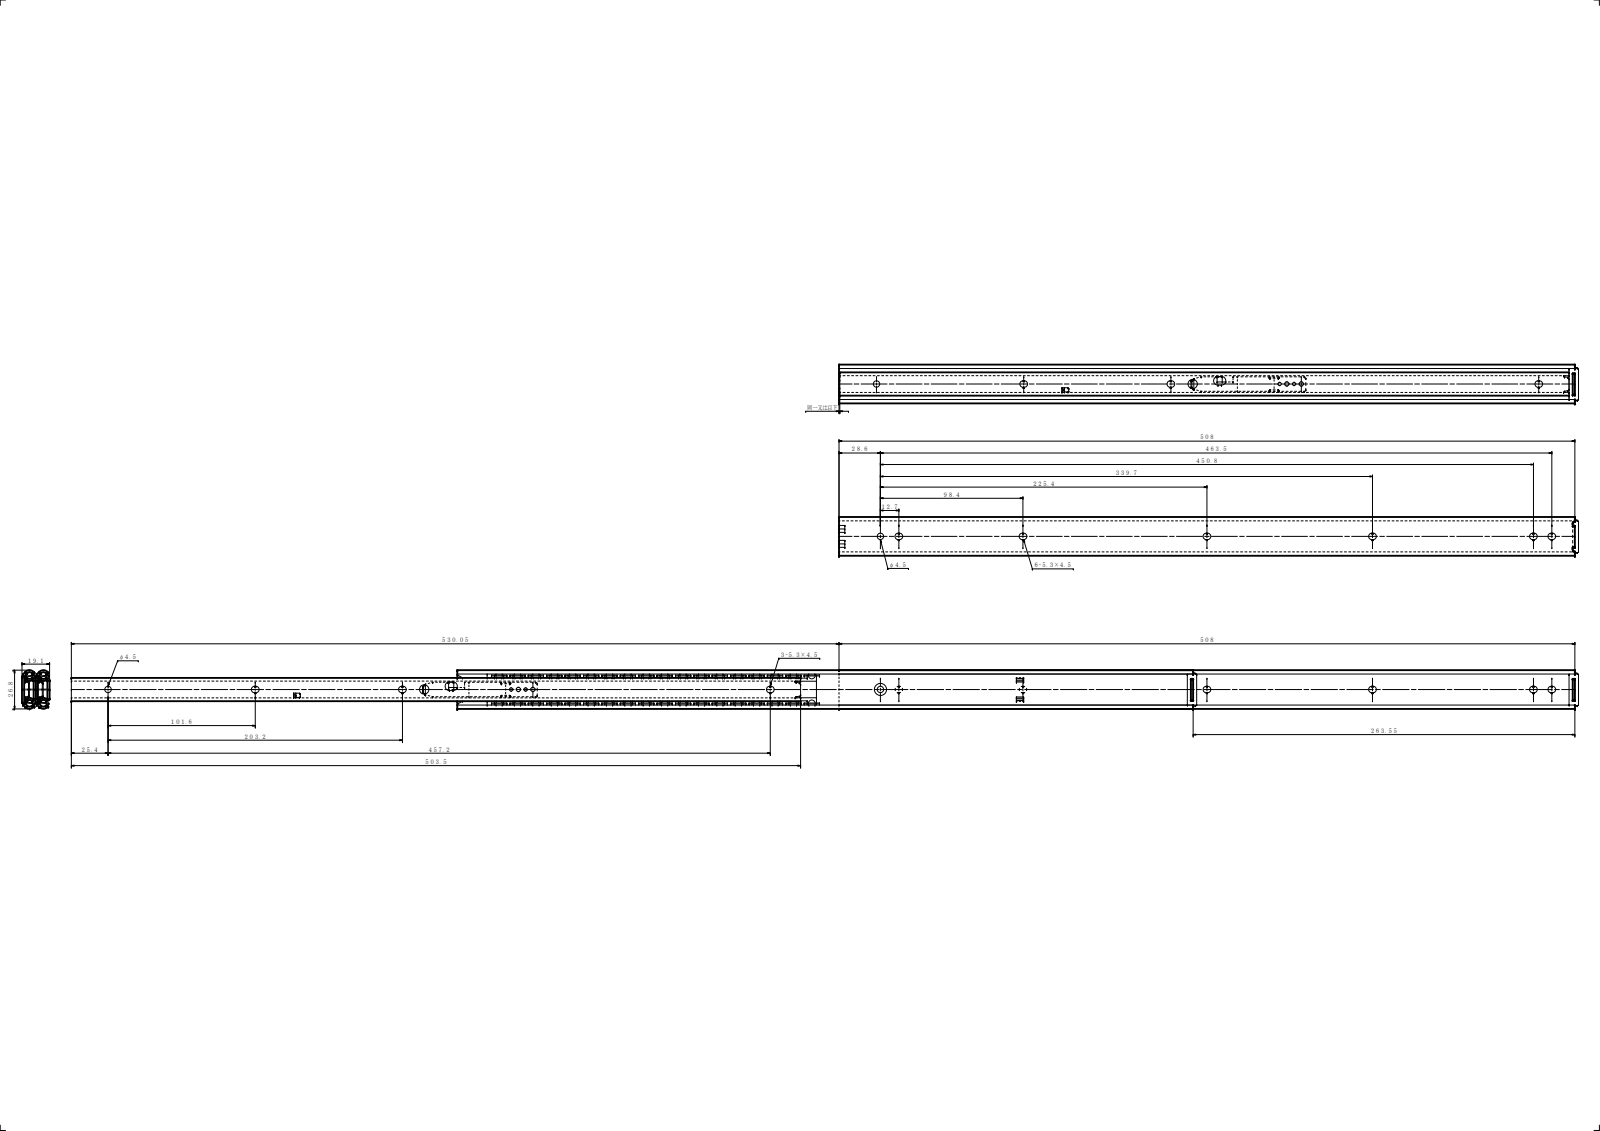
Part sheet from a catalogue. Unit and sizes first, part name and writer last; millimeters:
Units: millimetres
Overall size (bounding box): 1040.55 × 26.8 × 19.1
Round holes (diameter × count): ⌀4.2 ×4, ⌀2.34 ×2, ⌀3 ×2, ⌀3.03 ×2, ⌀4.5 ×2, ⌀4 ×1, ⌀6.5 ×1, ⌀8.5 ×1
Round bosses / shafts (diameter × count): ⌀4.5 ×2, ⌀4.3 ×2, ⌀3.9 ×2, ⌀2.3 ×2
Partial cylindrical surfaces — rounded edges, fillets, slot ends (radius × count): R0.2 ×24, R2 ×22, R2.25 ×18, R0.5 ×10, R2.38 ×8, R3.88 ×8, R3 ×7, R0.18 ×4
Main face-to-face distances: 1.5, 9.55, 8.05, 11.05, 17.6, 6.55, 16.1, 19.1, 3, 6.75
Hole centre spacings: 5, 10, 15, 22.76, 27.66, 32.59, 37.53, 38.13
Volume: 94 208 mm³ · Surface area: 133 961 mm²
Bodies: 12 solids, 426 faces (185 planar, 209 cylindrical, 32 other)
Part name (STEP PRODUCT): U2736-20 OM-B; SBP806 リードイン; SBP807（バネ圧縮）; U2736-20 OM-A (+5 more)
STEP written by: SolidWorks 2019 (CONFIG_CONTROL_DESIGN)
